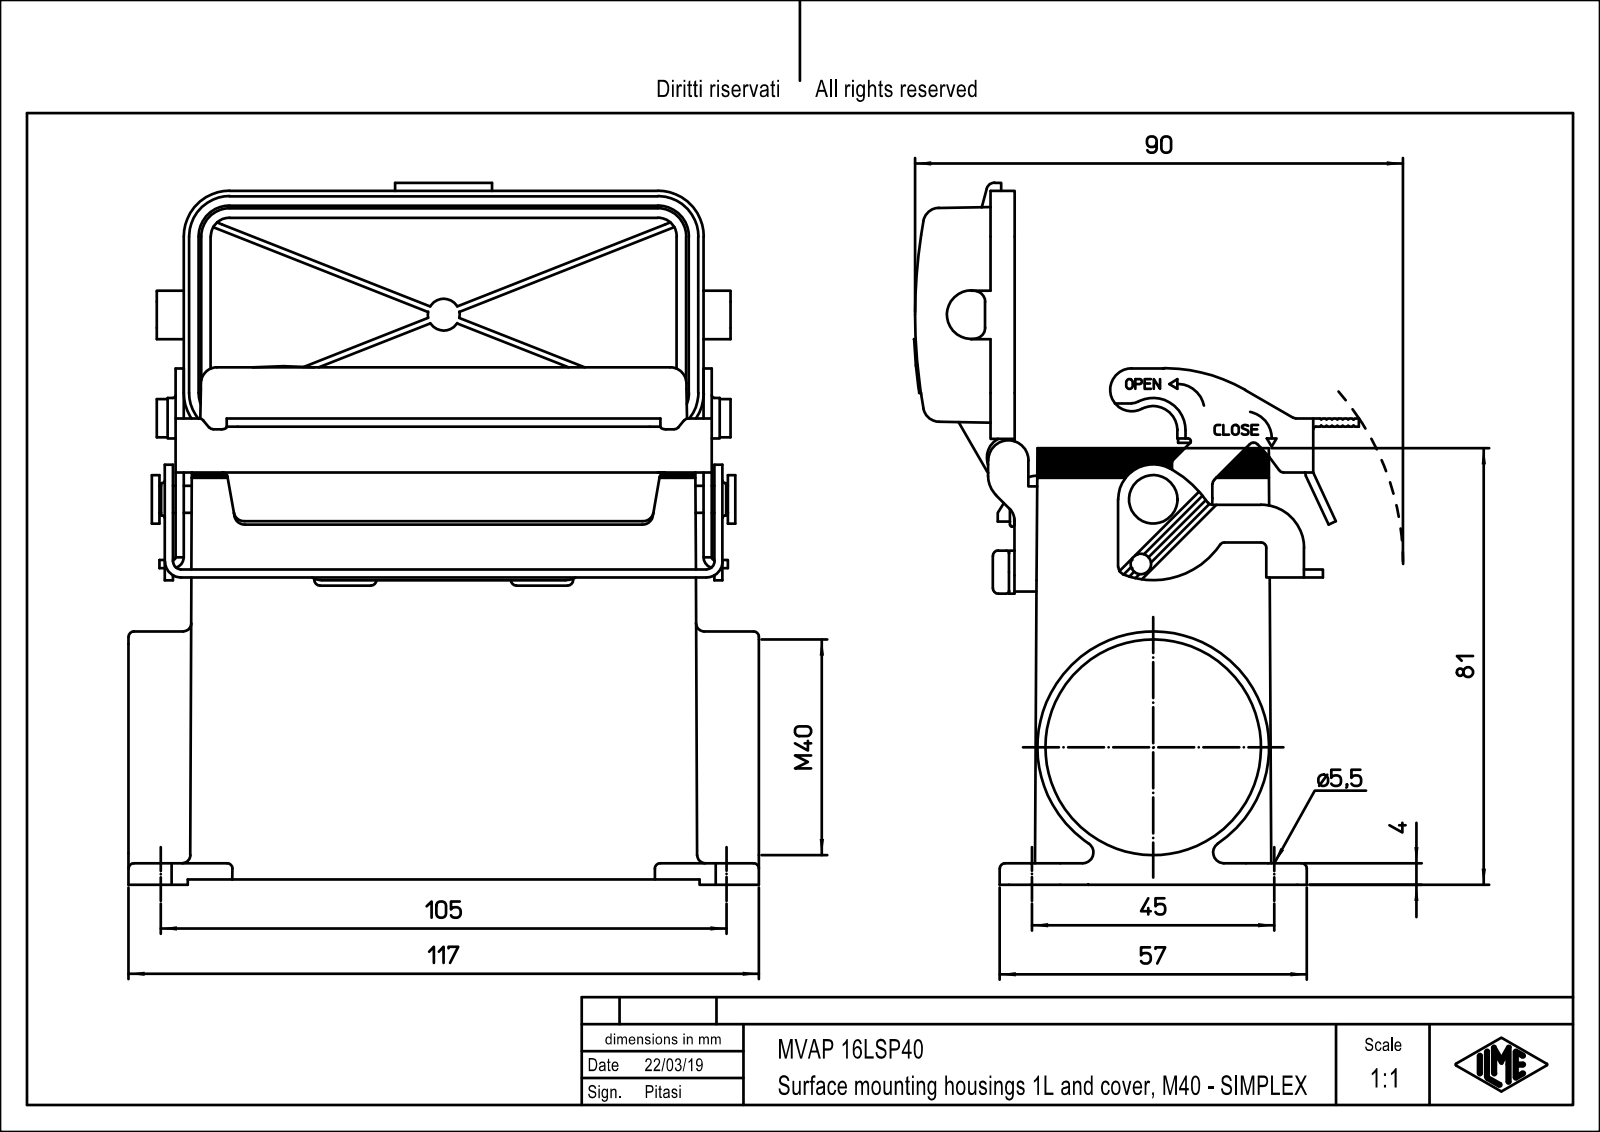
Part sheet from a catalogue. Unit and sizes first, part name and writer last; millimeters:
Units: millimetres
Overall size (bounding box): 126.72 × 117 × 79.7
Round holes (diameter × count): ⌀2.46 ×4, ⌀3 ×4, ⌀5.5 ×4, ⌀34 ×1, ⌀40 ×1
Round bosses / shafts (diameter × count): ⌀0.8 ×3, ⌀44.5 ×1, ⌀9 ×1, ⌀8.4 ×1, ⌀8 ×1, ⌀6 ×1, ⌀5 ×1, ⌀2.4 ×1
Partial cylindrical surfaces — rounded edges, fillets, slot ends (radius × count): R2 ×22, R3 ×13, R1.5 ×8, R3.5 ×7, R1 ×5, R6 ×5, R0.5 ×4, R1.8 ×4
Main face-to-face distances: 4, 40.5, 44.5, 36.5, 1.5, 7.5, 40.3, 11.5, 82, 6.65
Hole centre spacings: 16.43, 38.54, 91.69, 98.09, 27, 45, 77.5, 82.07
Volume: 139 931 mm³ · Surface area: 86 631 mm²
Bodies: 1 solid, 622 faces (385 planar, 213 cylindrical, 24 other)
Part name (STEP PRODUCT): MVAP_16LSP40
STEP written by: PTC Creo Elements/Direct Modeling 19.0E 27-Jun-2016 (C) Parametric Technology GmbH (AUTOMOTIVE_DESIGN)
